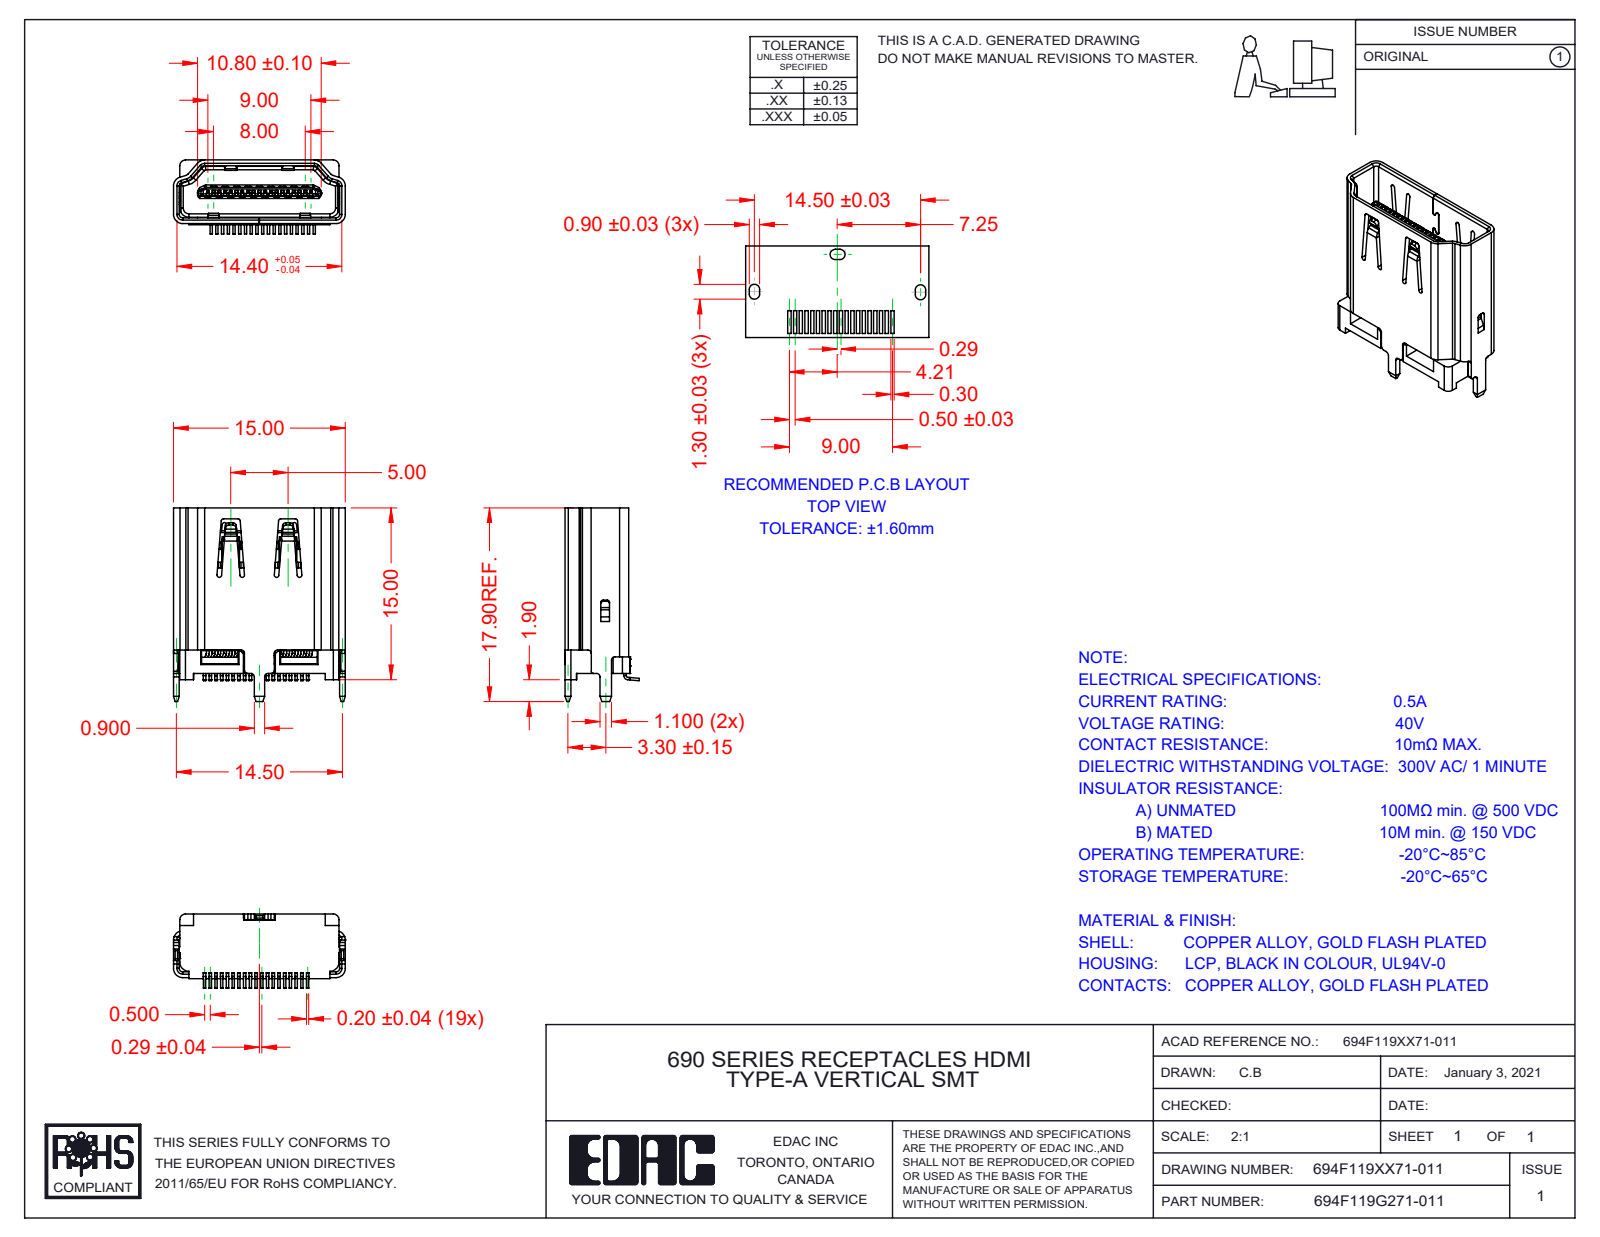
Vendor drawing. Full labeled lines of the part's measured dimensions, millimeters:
Part name (STEP PRODUCT): Shell 694F119XX71-011_Gold; Contacts 694F119XX71-011; Insulator 694F119XX71-011; 694F119G171-011
STEP written by: SolidWorks 2020 (AUTOMOTIVE_DESIGN)
Units: millimetres
Bodies: 21 solids, 3937 faces (2871 planar, 984 cylindrical, 82 other)
Overall size (bounding box): 16.9 × 15 × 6.47
Volume: 556 mm³ · Surface area: 2 337 mm²
Partial cylindrical surfaces — rounded edges, fillets, slot ends (radius × count): R0.3 ×61, R0.1 ×42, R0.2 ×40, R0.54 ×38, R0.15 ×35, R0.35 ×12, R0.8 ×8, R0.5 ×6
Main face-to-face distances: 0.5, 5.05, 5.55, 4.55, 0.55, 0.7, 2.52, 2.53, 0.35, 1
